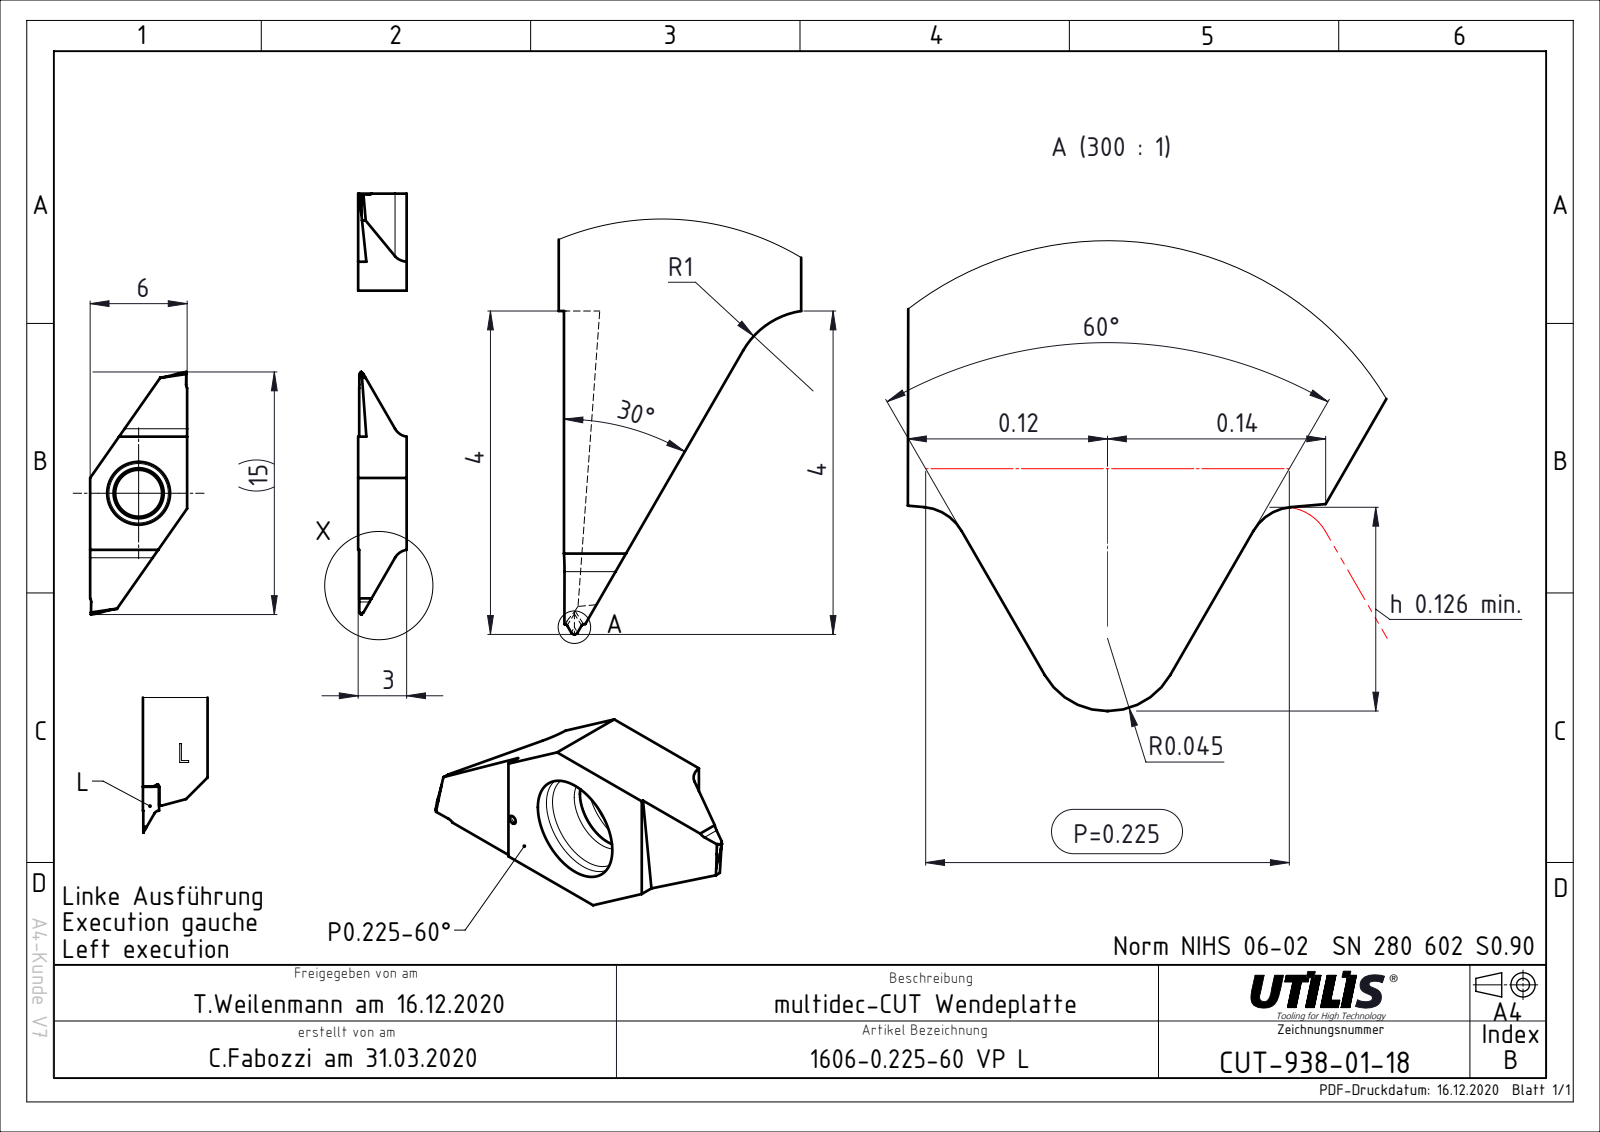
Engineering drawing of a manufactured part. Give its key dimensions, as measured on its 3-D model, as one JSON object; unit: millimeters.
{"part_name": "CUT-938-01; ASME Y14.5", "step_written_by": "FormatWorks Professional (AP242_MANAGED_MODEL_BASED_3D_ENGINEERING_MIM_LF)", "units": "millimeters", "bodies": {"solids": 1, "faces": 36, "planar": 22, "cylindrical": 14, "other": 0}, "overall_size": [15, 6, 3], "volume_mm3": 126, "surface_area_mm2": 210, "round_holes": [[2.9, 1]], "partial_cylinders_radius": [[1, 2]], "face_to_face_distances": [6, 3, 9, 7, 12, 7.22, 14.38]}
